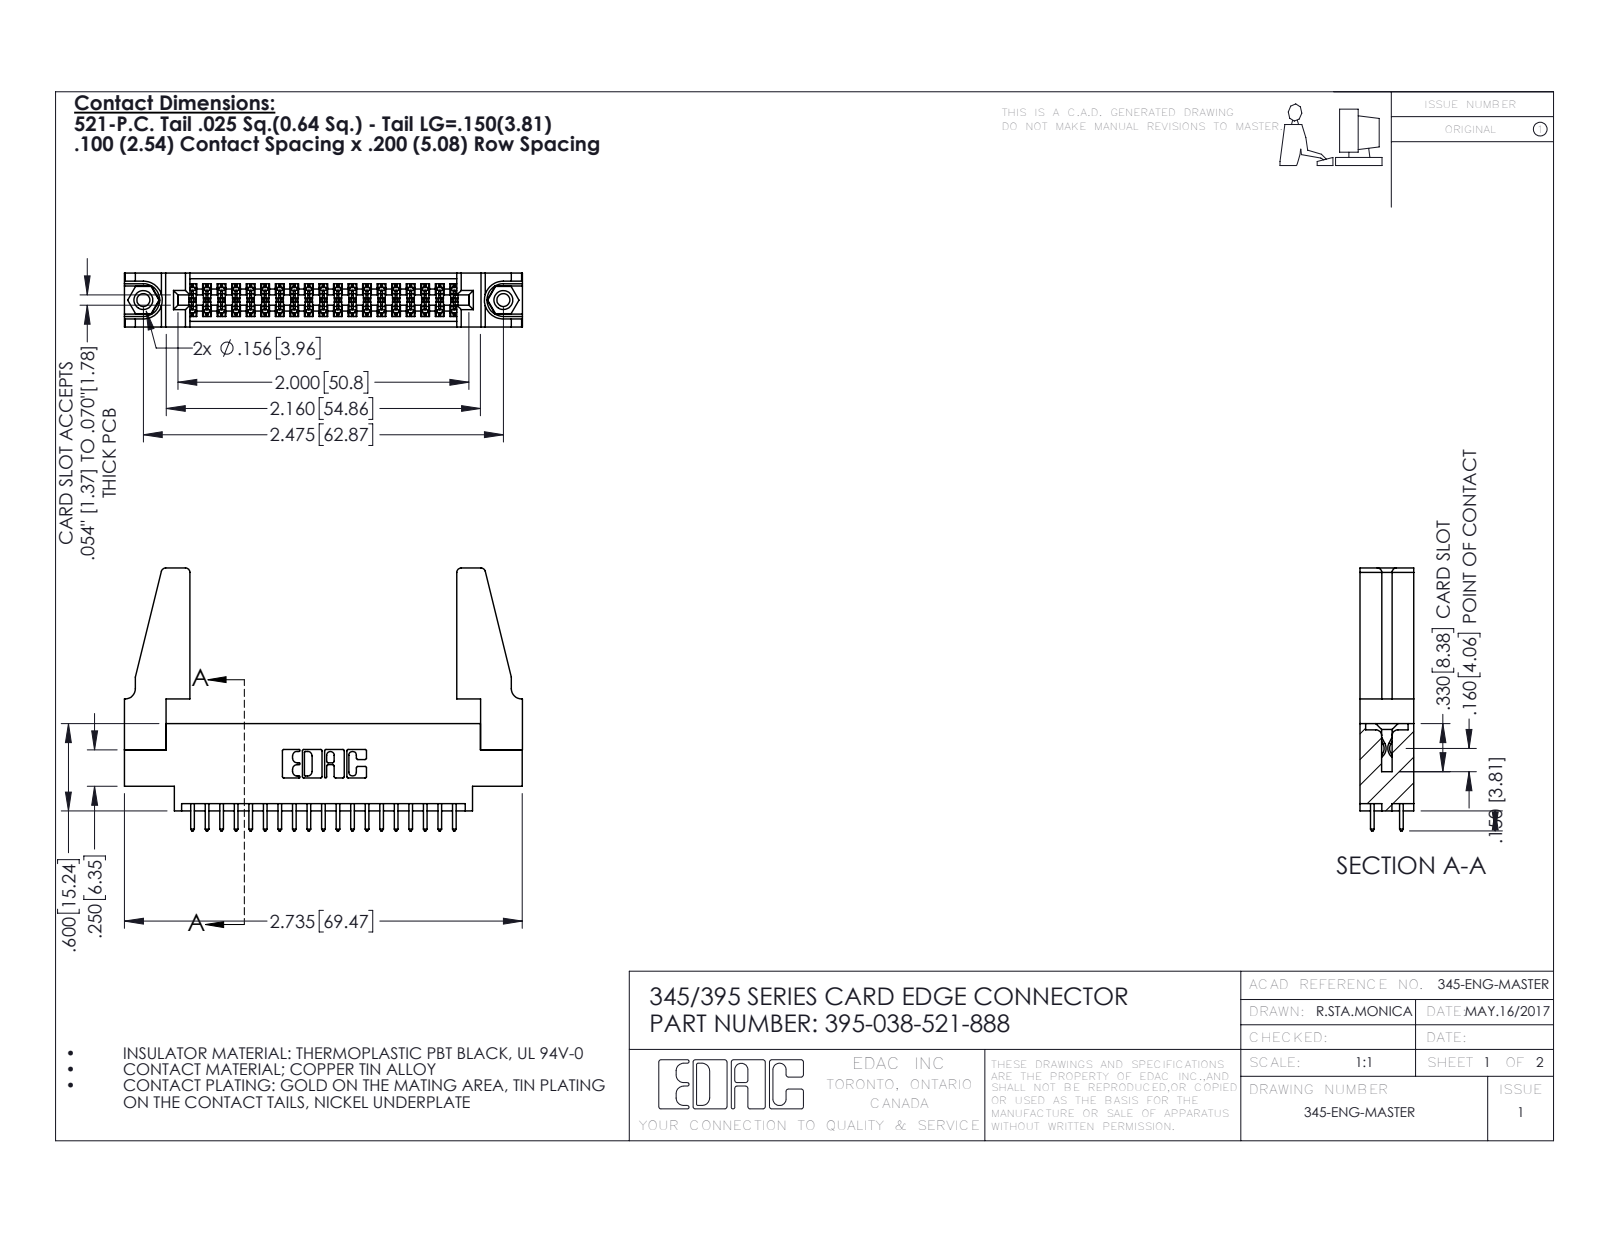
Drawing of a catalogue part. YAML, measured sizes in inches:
part_name: "395-038-521-888; 345 Part_0.170 Offset - 0.156 Dia-TH; 345-220-078_345-220-088; 345-292-001_345-293-121 (+1 more)"
step_written_by: "SolidWorks 2016 (CONFIG_CONTROL_DESIGN)"
units: inches
bodies: {solids: 43, faces: 2154, planar: 1410, cylindrical: 728, other: 16}
overall_size: [2.736, 1.807, 0.37]
volume: 0.59
surface_area: 18.9
round_holes:
  - {diameter: 0.089, count: 2}
  - {diameter: 0.125, count: 2}
  - {diameter: 0.156, count: 2}
  - {diameter: 0.064, count: 1}
round_bosses_or_shafts:
  - {diameter: 0.155, count: 2}
partial_cylinders:
  - {radius: 0.006, count: 57}
  - {radius: 0.01, count: 38}
  - {radius: 0.01, count: 22}
  - {radius: 0.03, count: 8}
  - {radius: 0.007, count: 6}
  - {radius: 0.031, count: 6}
  - {radius: 0.026, count: 3}
  - {radius: 0.014, count: 2}
face_to_face_distances: [0.37, 0.072, 0.298, 0.2, 0.098, 0.272, 0.025, 0.225, 0.175, 0.148]
hole_center_spacings: [0.27, 2.241, 2.475]
